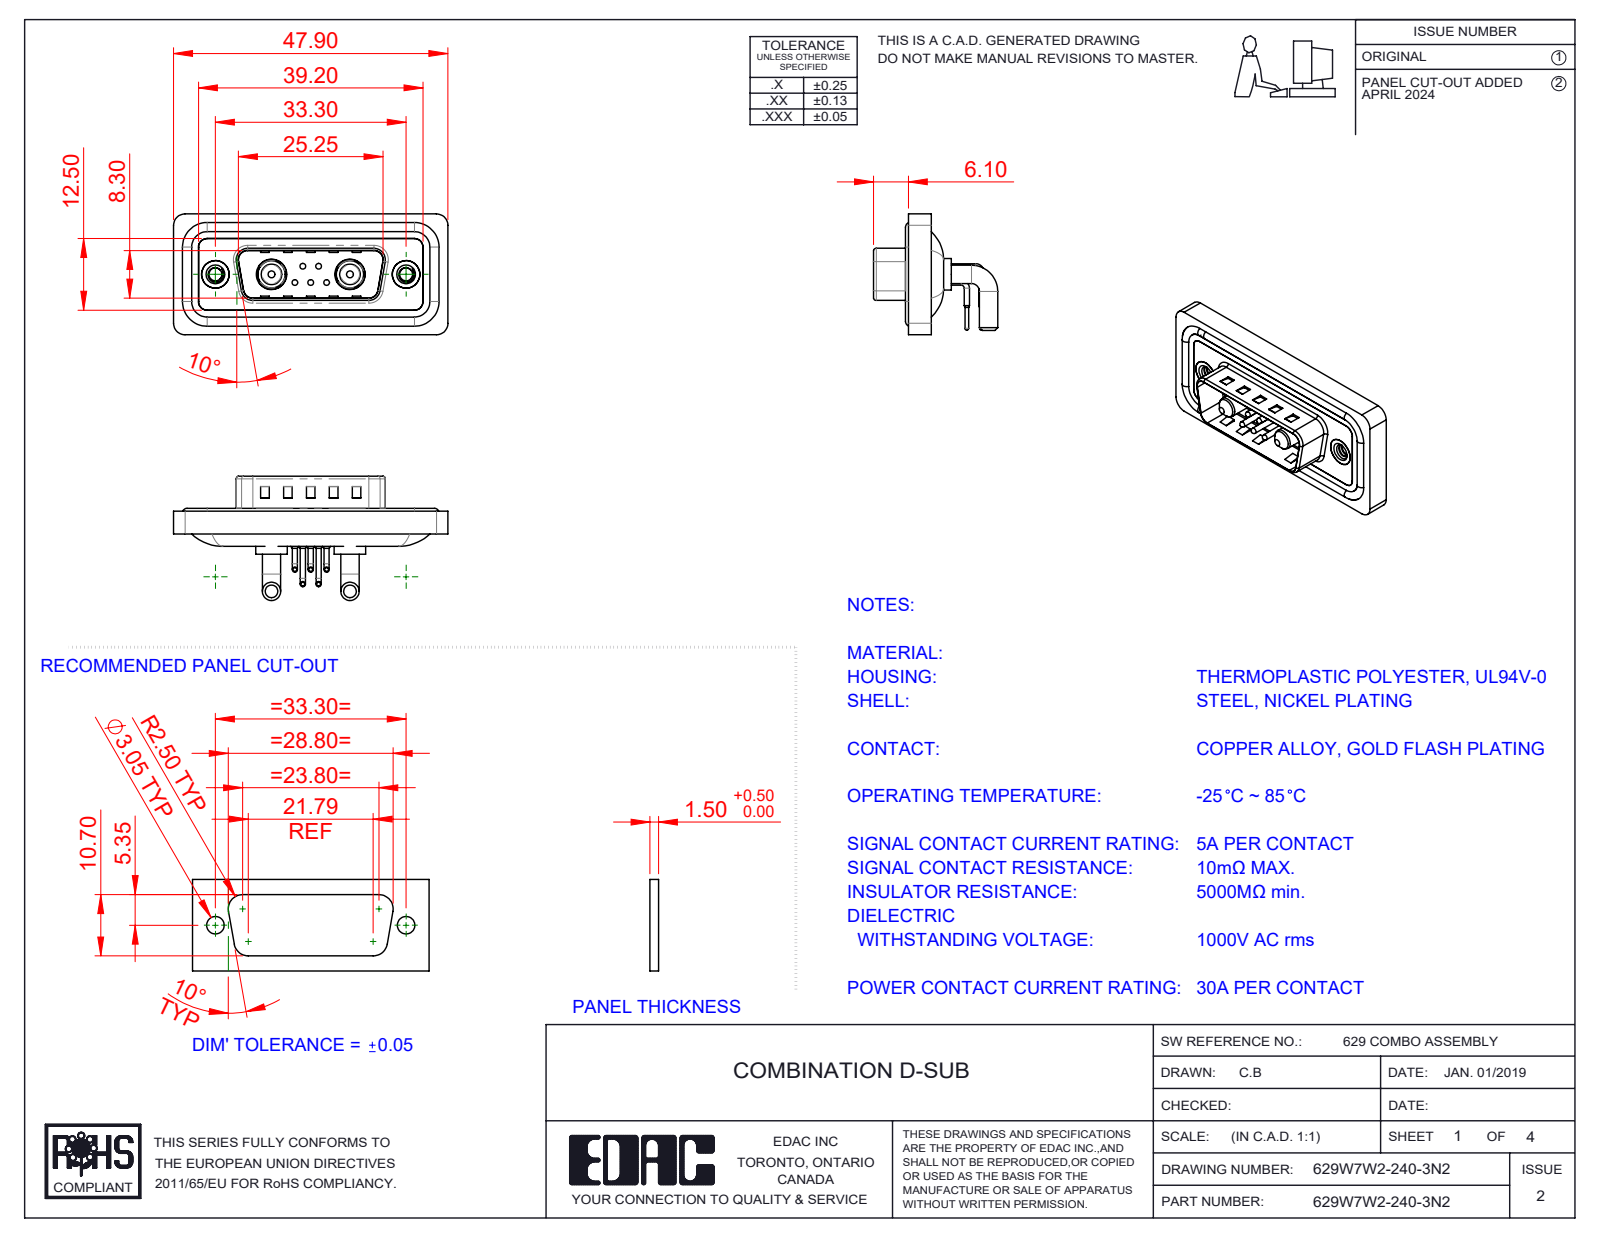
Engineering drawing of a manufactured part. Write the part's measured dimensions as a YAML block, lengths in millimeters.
part_name: "629W7W2-240-3N2; 629Combo Shell Rear_15 Contacts; Power Pin_30A RA; 629Combo Threaded Rivet_2 (+5 more)"
step_written_by: "SolidWorks 2023 (CONFIG_CONTROL_DESIGN)"
units: millimeters
bodies: {solids: 16, faces: 1083, planar: 517, cylindrical: 406, other: 160}
overall_size: [47.9, 21.7, 21.1]
volume: 5748
surface_area: 9178
round_holes:
  - {diameter: 0.75, count: 5}
  - {diameter: 1.6, count: 5}
  - {diameter: 2, count: 5}
  - {diameter: 2.26, count: 2}
  - {diameter: 4, count: 2}
  - {diameter: 4.8, count: 2}
  - {diameter: 4.85, count: 2}
  - {diameter: 5, count: 2}
  - {diameter: 5.3, count: 2}
round_bosses_or_shafts:
  - {diameter: 0.9, count: 10}
  - {diameter: 1.5, count: 5}
  - {diameter: 1, count: 5}
  - {diameter: 0.65, count: 5}
  - {diameter: 3.2, count: 4}
  - {diameter: 1.6, count: 4}
  - {diameter: 5.5, count: 2}
  - {diameter: 5.2, count: 2}
partial_cylinders:
  - {radius: 2, count: 20}
  - {radius: 1.5, count: 18}
  - {radius: 0.5, count: 8}
  - {radius: 1.6, count: 8}
  - {radius: 1.01, count: 5}
  - {radius: 0.25, count: 4}
  - {radius: 0.6, count: 4}
  - {radius: 0.65, count: 4}
face_to_face_distances: [0.4, 2.9, 0.8, 1.1, 2.1, 1.6, 2.5, 3.1, 4.5, 4.1]
hole_center_spacings: [3.16, 2.77, 9.8, 23.5, 4.31, 4.33, 5.03, 5.04]
